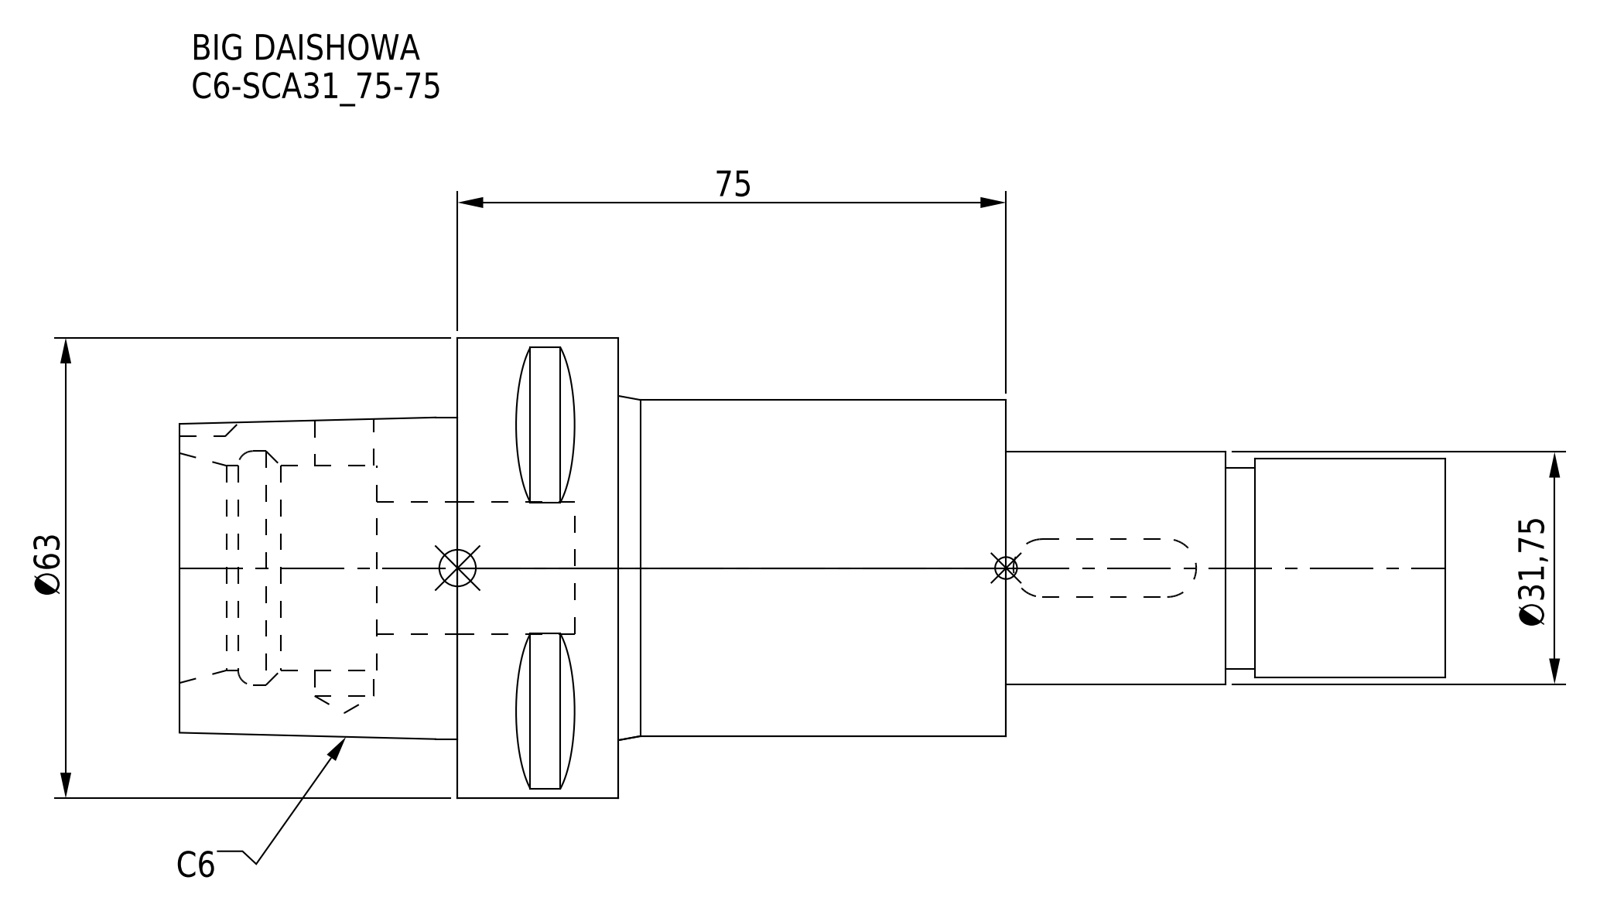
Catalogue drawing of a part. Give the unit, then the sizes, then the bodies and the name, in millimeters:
Units: millimetres
Overall size (bounding box): 173 × 63 × 63
Round holes (diameter × count): ⌀8.1 ×1, ⌀18 ×1, ⌀28 ×1, ⌀32 ×1
Round bosses / shafts (diameter × count): ⌀63 ×1, ⌀46 ×1, ⌀31.75 ×1, ⌀30 ×1, ⌀27.5 ×1
Partial cylindrical surfaces — rounded edges, fillets, slot ends (radius × count): R3.96 ×2, R5 ×1
Main face-to-face distances: 22, 60, 113, 53, 75, 135, 27, 173, 38, 30
Volume: 229 859 mm³ · Surface area: 33 949 mm²
Bodies: 1 solid, 71 faces (34 planar, 25 cylindrical, 12 other)
Part name (STEP PRODUCT): C6-SCA31_75-75
STEP written by: CREO PARAMETRIC BY PTC INC, 2016380 (AUTOMOTIVE_DESIGN)
